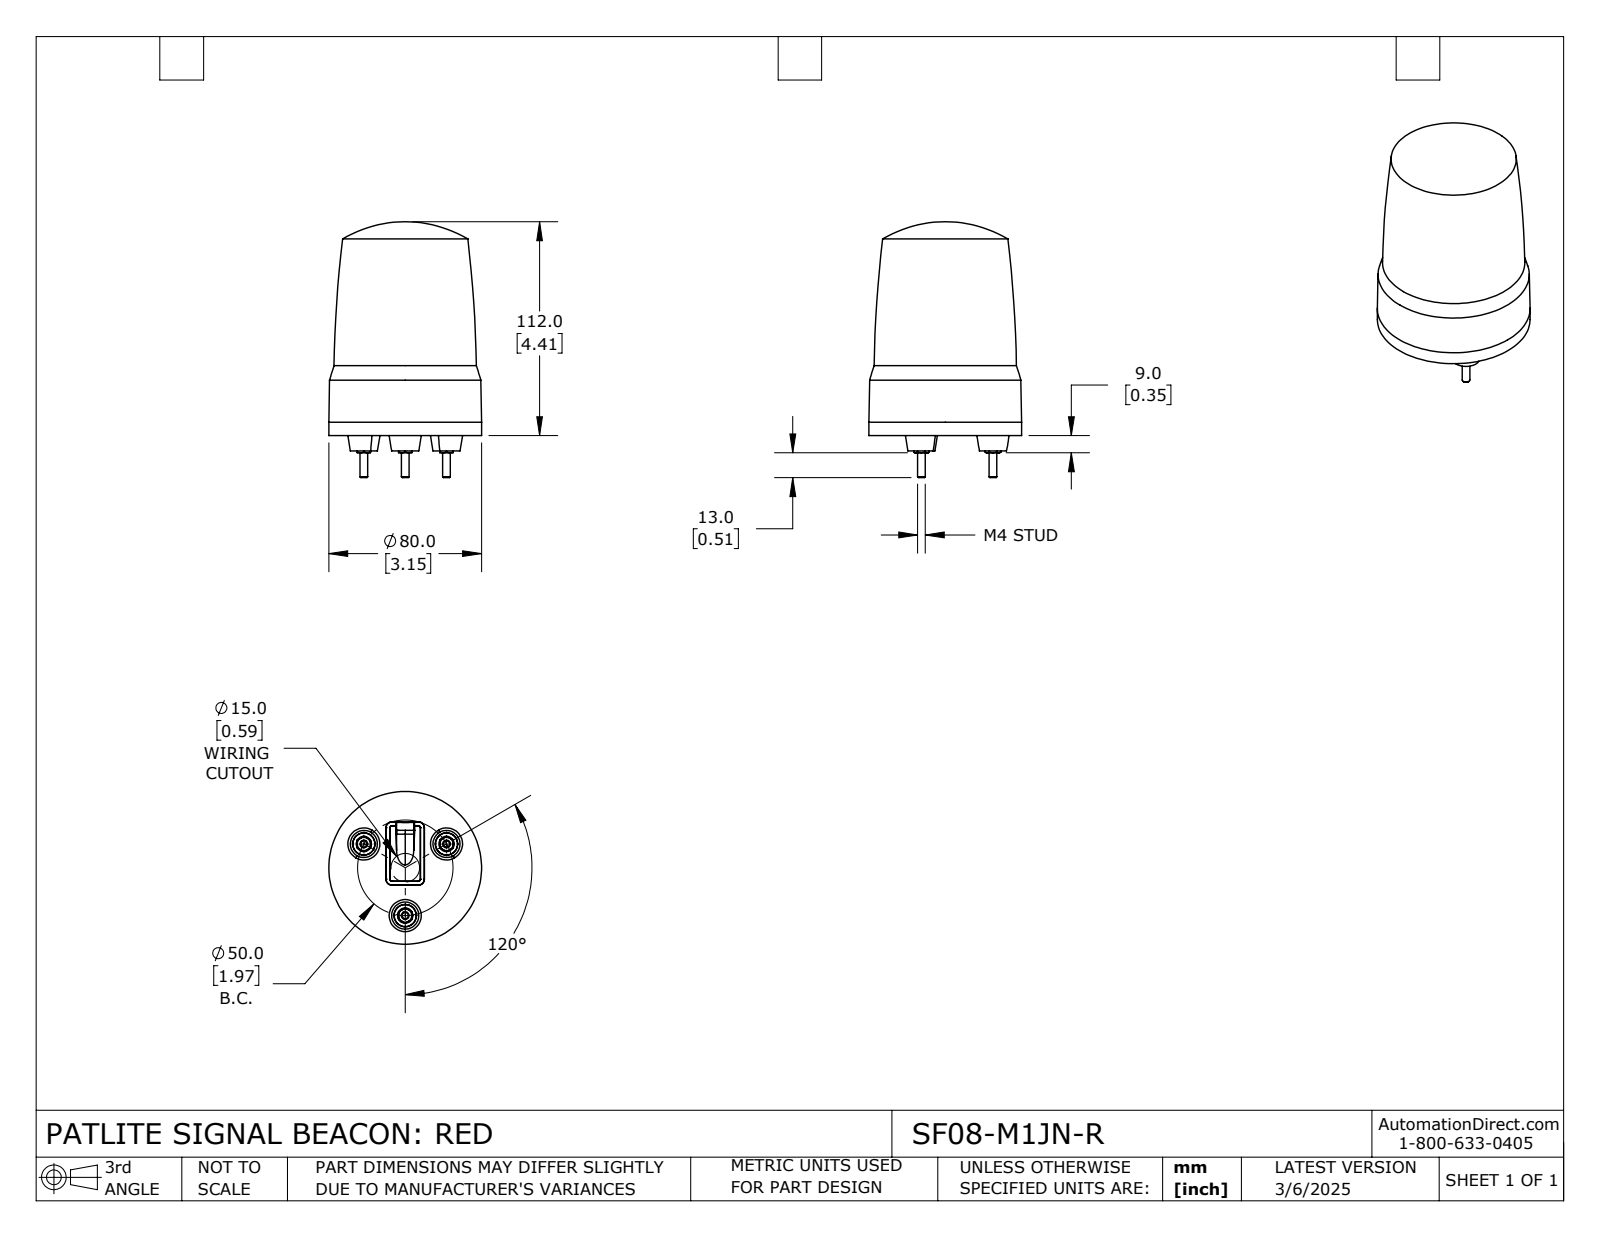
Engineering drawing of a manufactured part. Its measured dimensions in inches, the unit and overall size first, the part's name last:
Units: inches
Overall size (bounding box): 5.276 × 3.15 × 3.15
Round bosses / shafts (diameter × count): ⌀0.315 ×3, ⌀0.157 ×3, ⌀3.15 ×1
Main face-to-face distances: 0.033, 0.096, 0.063, 0.209, 0.242, 0.305, 0.106, 0.315, 0.348, 0.411
Volume: 28.27 in³ · Surface area: 54.88 in²
Bodies: 1 solid, 138 faces (47 planar, 14 cylindrical, 77 other)
Part name (STEP PRODUCT): SF08-M1JN-R
STEP written by: SolidWorks 2024 (CONFIG_CONTROL_DESIGN)
